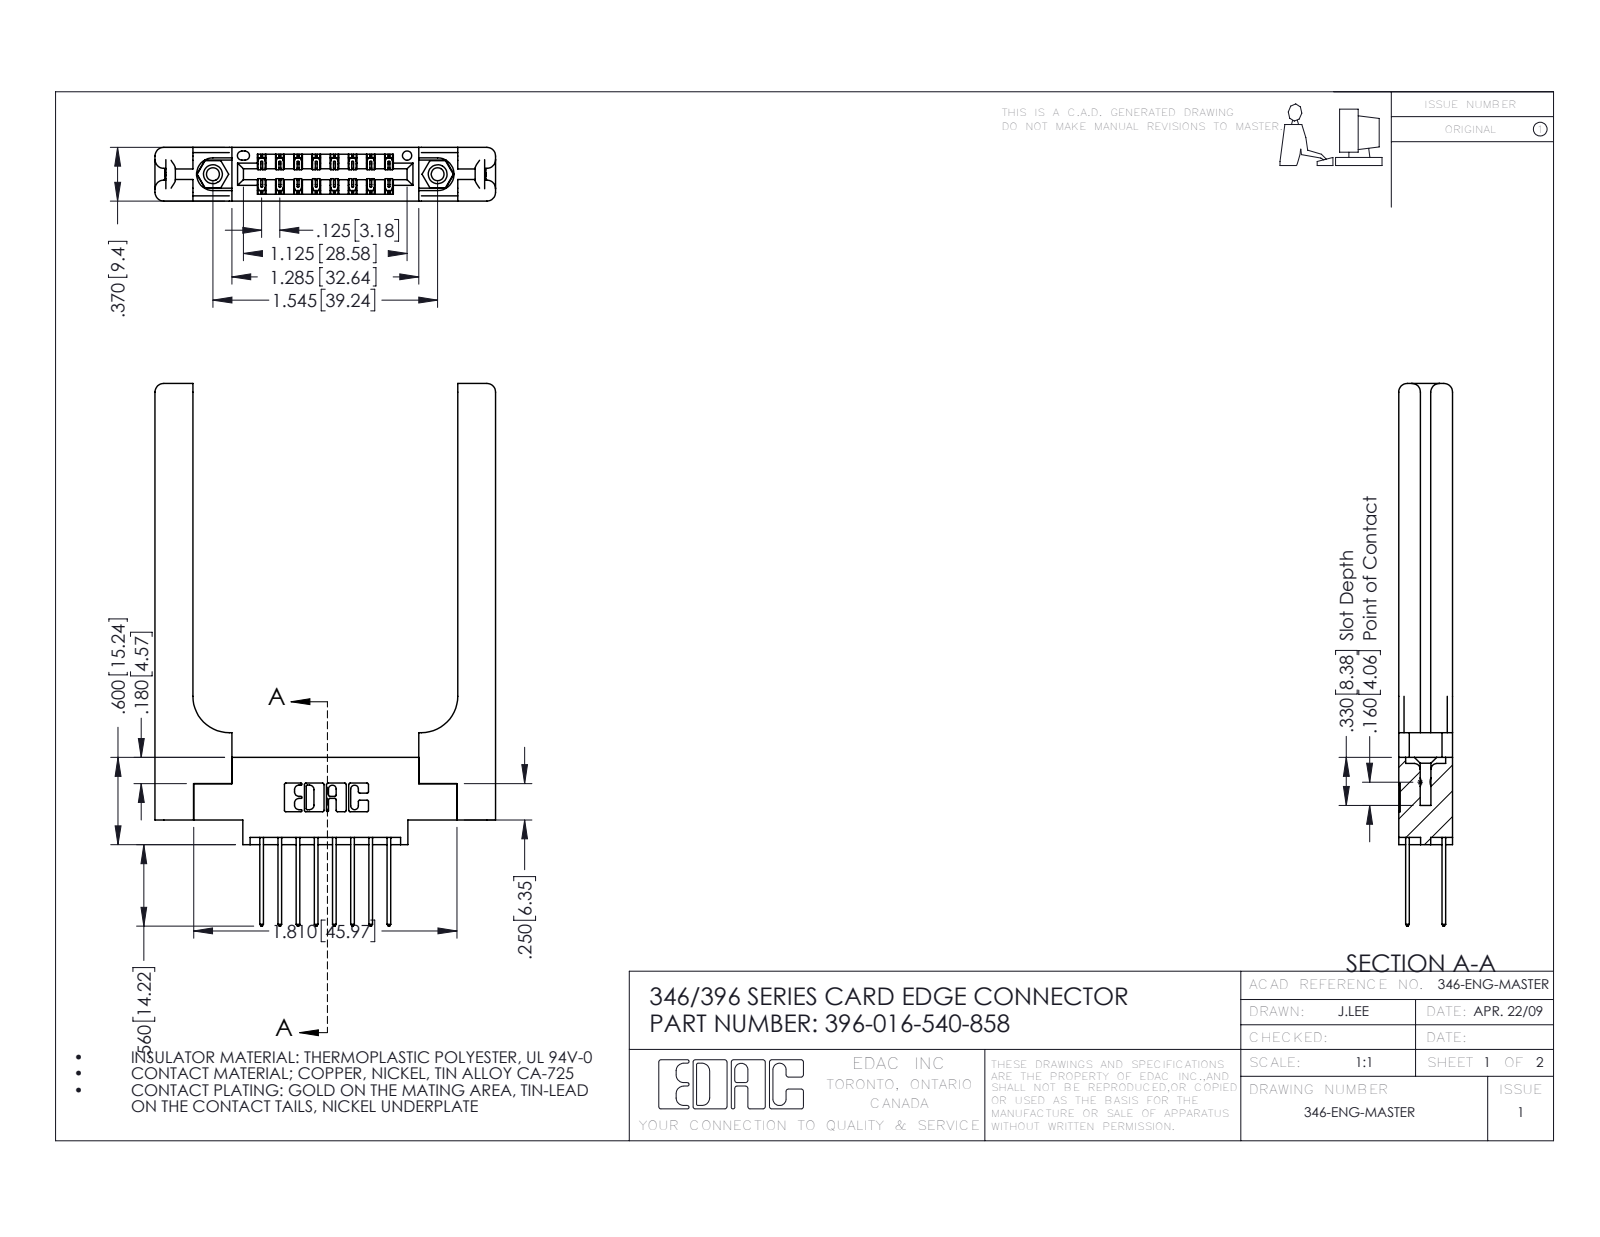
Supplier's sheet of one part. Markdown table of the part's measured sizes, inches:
| quantity | value |
| --- | --- |
| part name | 345-250-001_345-250-001-102; 345-292-001_345-293-140; 346 Part_0.170 Offset - 0.156 Dia-TH; 396-016-540-858 (+1 more) |
| STEP written by | SolidWorks 2016 (CONFIG_CONTROL_DESIGN) |
| units | inches |
| bodies | 21 solids, 1214 faces (788 planar, 366 cylindrical, 60 other) |
| overall size | 3.73 × 2.341 × 0.37 |
| volume | 0.789 in³ |
| surface area | 19.19 in² |
| round holes (diameter × count) | 0.089 × 2, 0.125 × 2, 0.156 × 2, 0.064 × 1 |
| round bosses / shafts (diameter × count) | 0.155 × 2 |
| partial cylindrical surfaces (radius × count) | 0.006 × 24, 0.01 × 22, 0.01 × 16, 0.06 × 16, 0.007 × 6, 0.031 × 6, 0.026 × 3, 0.014 × 2 |
| main face-to-face distances | 0.37, 0.15, 0.072, 0.148, 0.22, 0.25, 0.102, 0.048, 0.322, 0.173 |
| hole center spacings | 0.246, 1.341, 1.545 |
